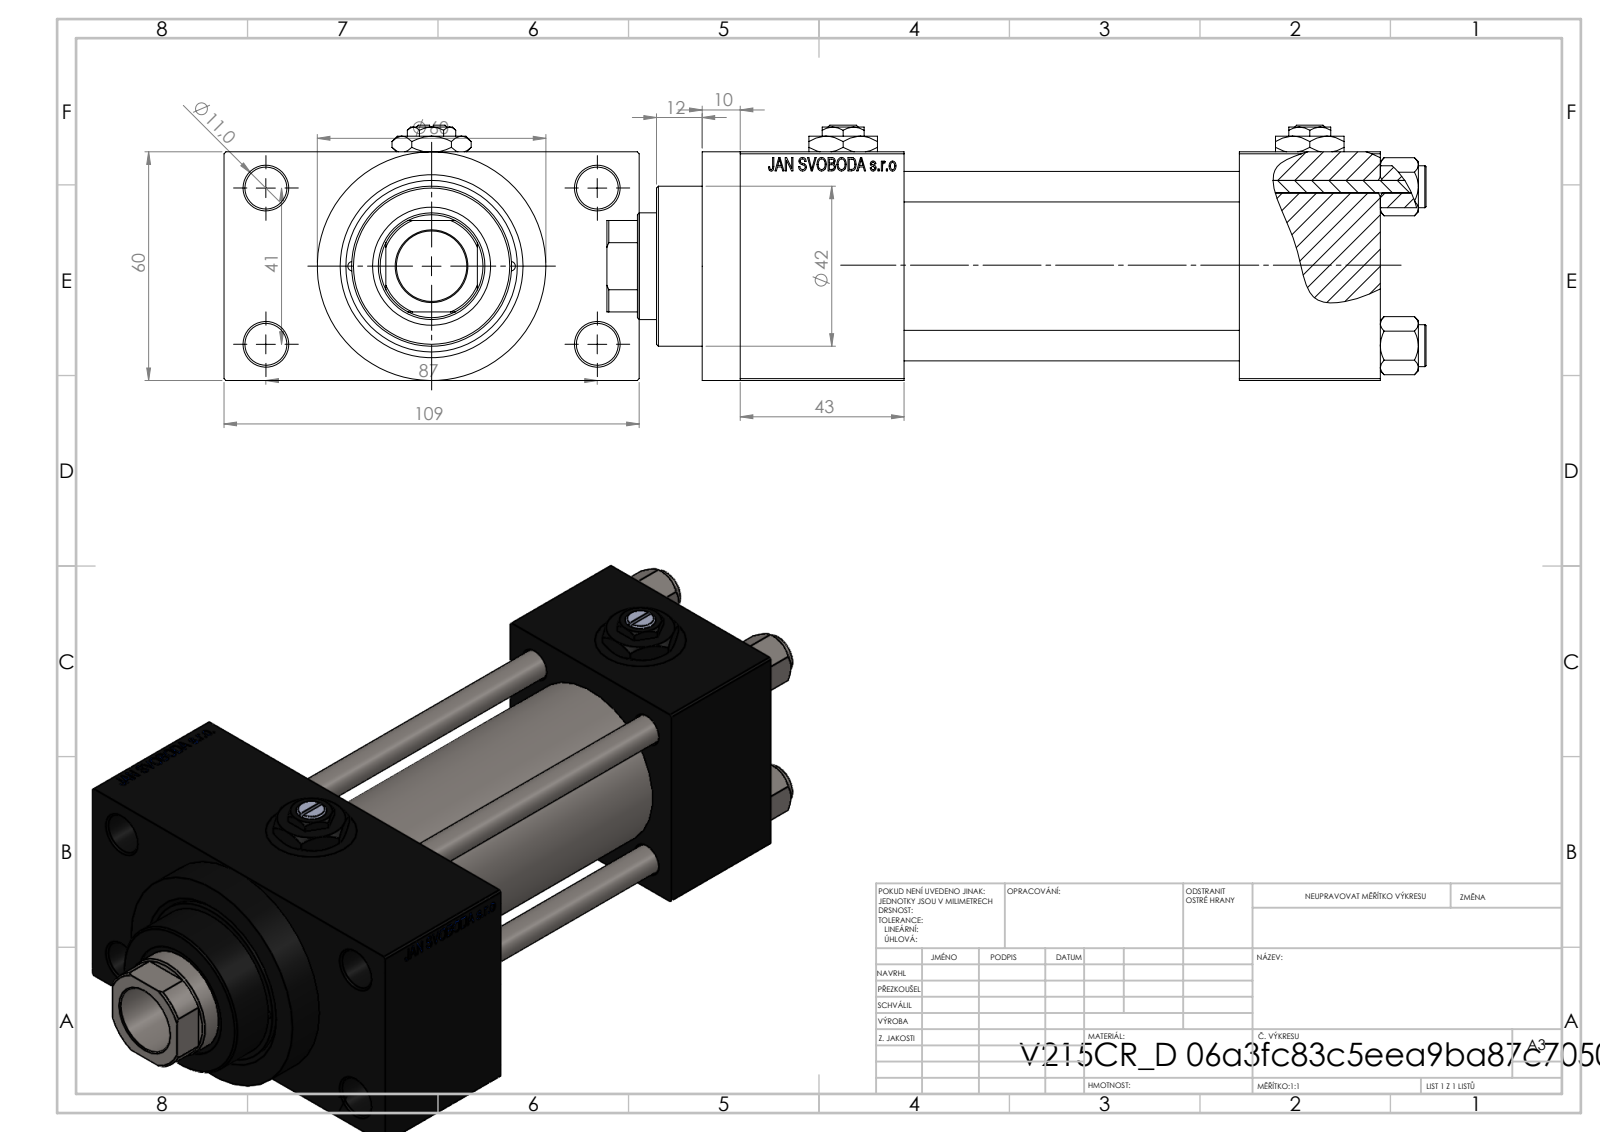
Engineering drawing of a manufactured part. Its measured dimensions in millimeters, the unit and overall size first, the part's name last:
Units: millimetres
Overall size (bounding box): 215 × 109 × 67
Round holes (diameter × count): ⌀8 ×4, ⌀11 ×4, ⌀16.66 ×4, ⌀24 ×4, ⌀7 ×3, ⌀2.5 ×2, ⌀18.5 ×1, ⌀28 ×1, ⌀31 ×1, ⌀40 ×1, ⌀45 ×1
Round bosses / shafts (diameter × count): ⌀11 ×4, ⌀60 ×1, ⌀46 ×1, ⌀42 ×1
Partial cylindrical surfaces — rounded edges, fillets, slot ends (radius × count): R13.5 ×1
Main face-to-face distances: 60, 24.5, 88, 84.5, 37, 125, 168, 131, 43, 109
Hole centre spacings: 20.85, 22.65, 29.49, 30.62, 41.7, 46.53, 47.15, 48.09
Volume: 563 142 mm³ · Surface area: 145 481 mm²
Bodies: 13 solids, 1215 faces (550 planar, 103 cylindrical, 562 other)
Part name (STEP PRODUCT): V215CR_D_TYCINKA; V215_VC_A; V215CR_D_Body; NUT_M5_D (+2 more)
STEP written by: SolidWorks 2019 (CONFIG_CONTROL_DESIGN)
